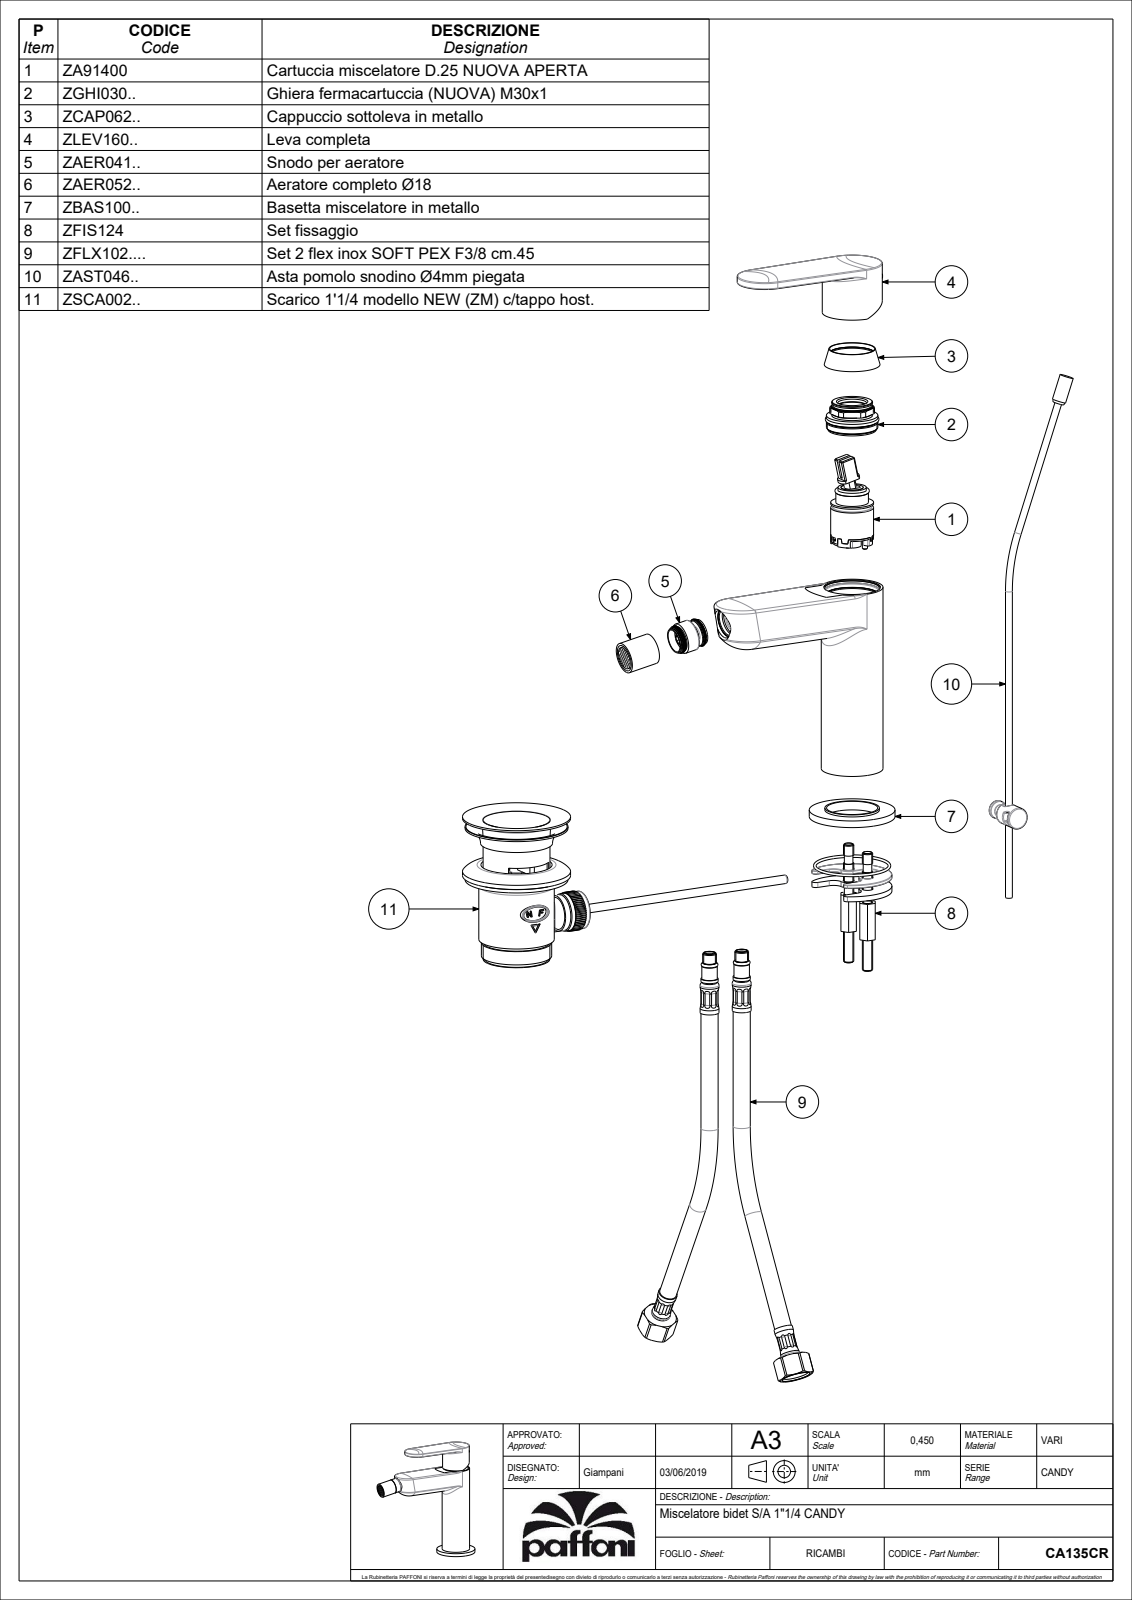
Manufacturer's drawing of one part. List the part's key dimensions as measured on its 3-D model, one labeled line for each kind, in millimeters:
Part name (STEP PRODUCT): CA135CR
STEP written by: CREO PARAMETRIC BY PTC INC, 2020044 (CONFIG_CONTROL_DESIGN)
Units: millimetres
Bodies: 3 solids, 186 faces (50 planar, 54 cylindrical, 82 other)
Overall size (bounding box): 149.24 × 145.92 × 50
Volume: 208 735 mm³ · Surface area: 42 392 mm²
Round holes (diameter × count): ⌀3 ×1, ⌀4.5 ×1, ⌀16.7 ×1, ⌀24.8 ×1, ⌀26.2 ×1, ⌀28 ×1
Round bosses / shafts (diameter × count): ⌀50 ×1, ⌀36 ×1, ⌀35 ×1, ⌀18 ×1, ⌀16 ×1, ⌀14.5 ×1, ⌀10 ×1, ⌀8 ×1
Partial cylindrical surfaces — rounded edges, fillets, slot ends (radius × count): R3 ×4, R3.5 ×1, R16 ×1
Main face-to-face distances: 4, 114, 110, 142.92, 138.92, 28.92, 2.5, 11.5, 9, 24.5
